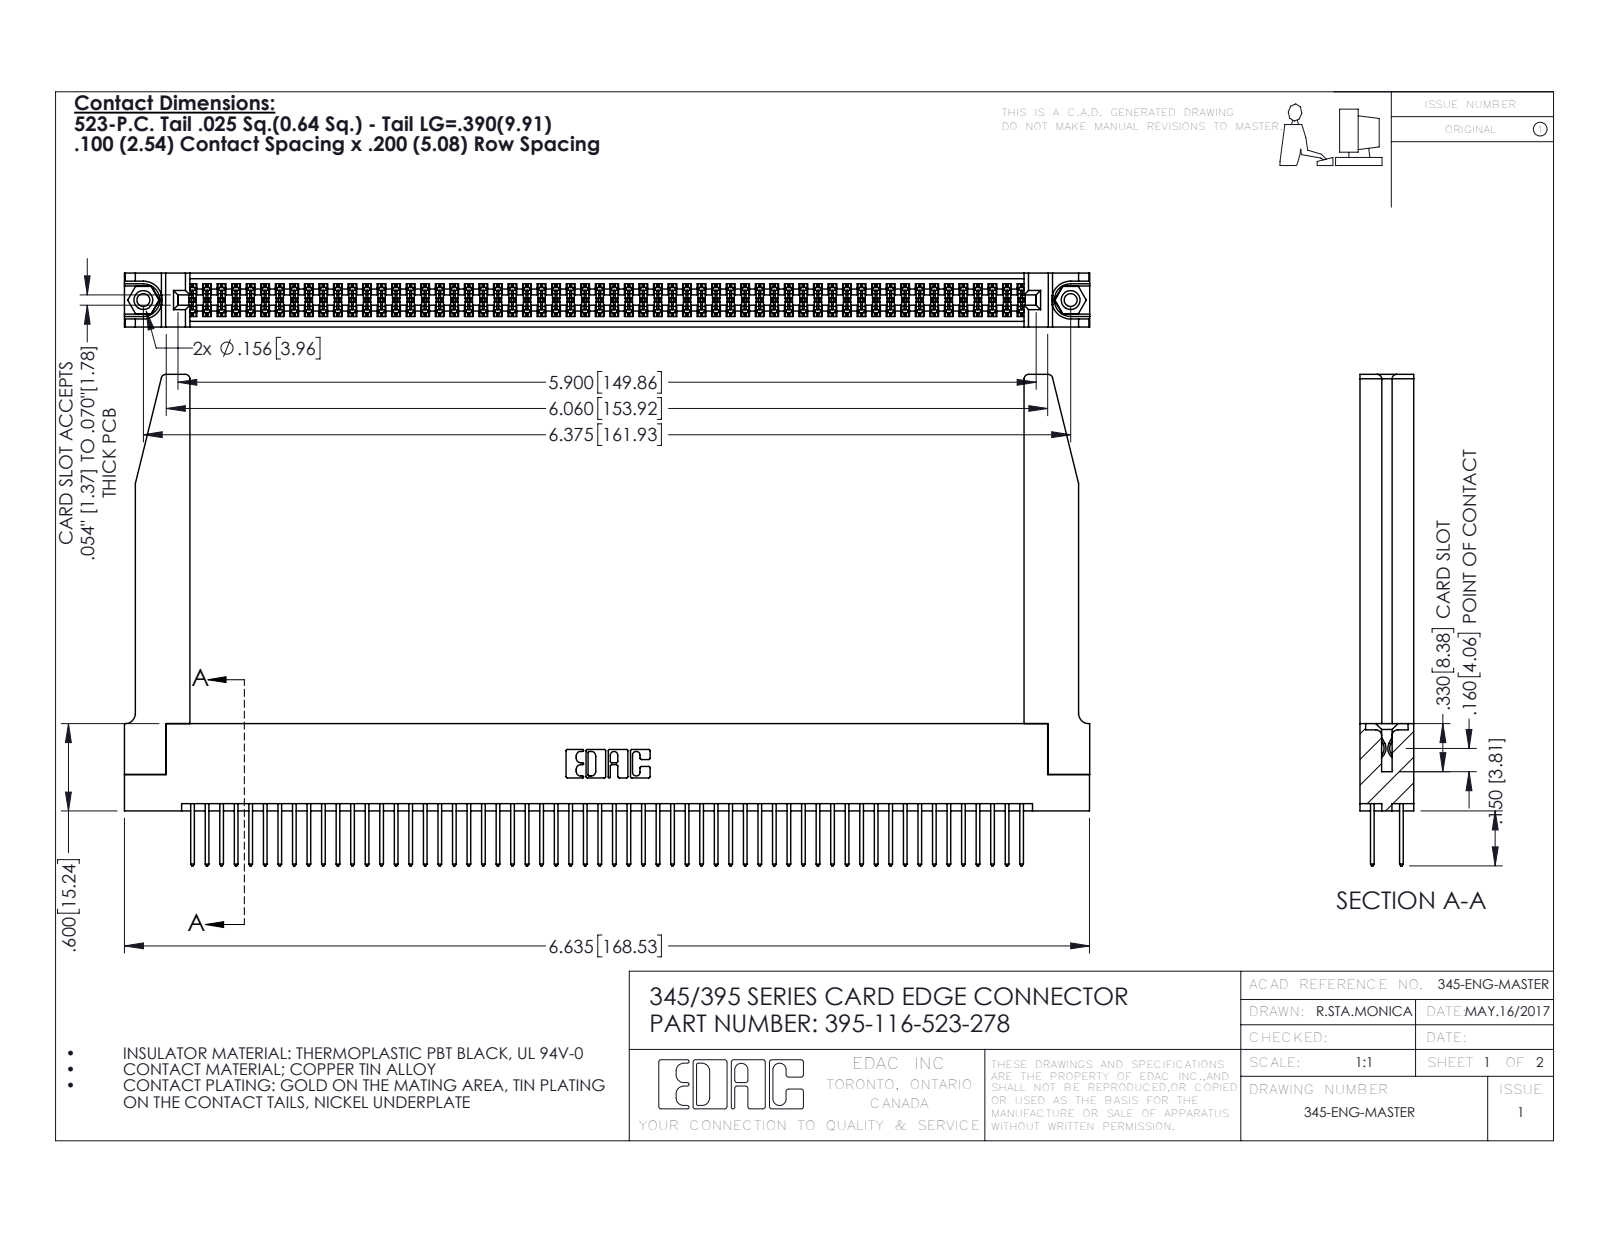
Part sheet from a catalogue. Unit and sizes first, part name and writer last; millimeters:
Units: millimetres
Overall size (bounding box): 168.6 × 85.8 × 9.4
Round holes (diameter × count): ⌀2.3 ×2, ⌀3.2 ×2, ⌀4 ×2, ⌀1.6 ×1
Round bosses / shafts (diameter × count): ⌀3.9 ×2
Partial cylindrical surfaces — rounded edges, fillets, slot ends (radius × count): R0.2 ×174, R0.3 ×116, R0.3 ×22, R0.8 ×8, R0.2 ×6, R0.8 ×6, R0.7 ×3, R0.4 ×2
Main face-to-face distances: 1.8, 7.6, 9.4, 5.1, 2.5, 6.9, 0.6, 5.7, 4.4, 3.8
Hole centre spacings: 6.9, 155.9, 161.9
Volume: 24 530 mm³ · Surface area: 32 990 mm²
Bodies: 121 solids, 6160 faces (4050 planar, 2058 cylindrical, 52 other)
Part name (STEP PRODUCT): 345-292-001_345-293-123; 345-220-078_345-220-078; 395-116-523-278; 345 Part_Flush Mounting Lugs - 0.156 Dia-TH (+1 more)
STEP written by: SolidWorks 2016 (CONFIG_CONTROL_DESIGN)
